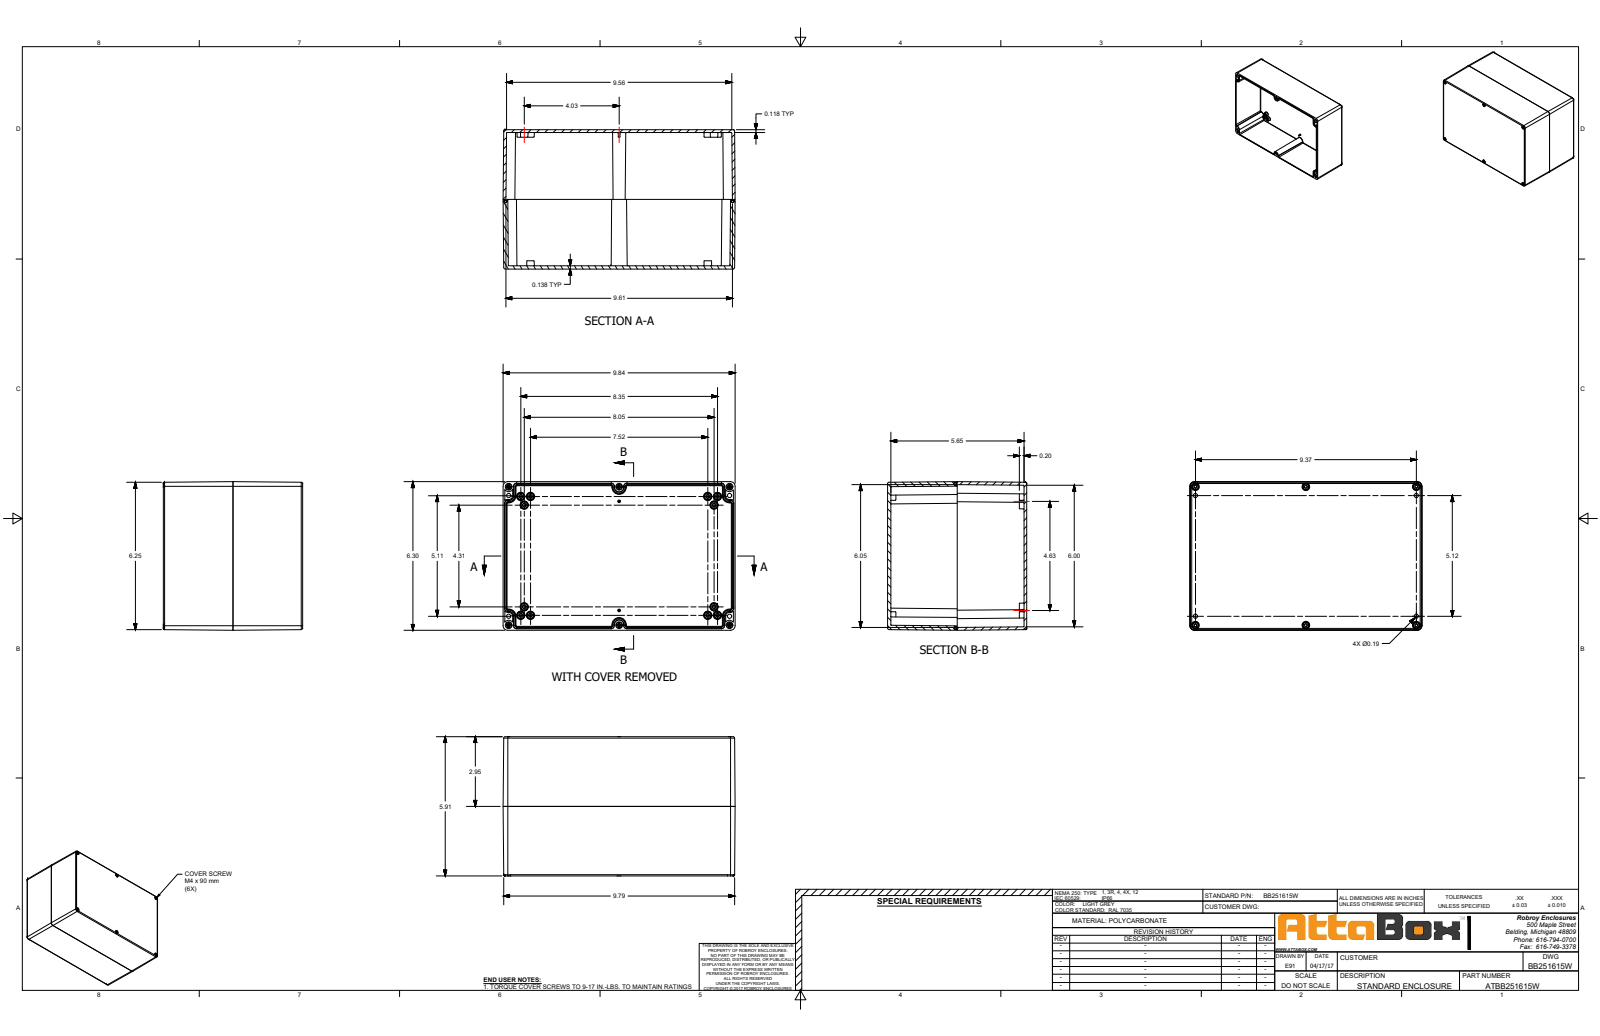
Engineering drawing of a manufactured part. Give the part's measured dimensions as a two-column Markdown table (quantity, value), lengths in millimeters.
| quantity | value |
| --- | --- |
| part name | BB251615W |
| STEP written by | SolidWorks 2018 (AUTOMOTIVE_DESIGN) |
| units | millimeters |
| bodies | 15 solids, 2307 faces (907 planar, 626 cylindrical, 774 other) |
| overall size | 250 × 160 × 150 |
| volume | 778 100 mm³ |
| surface area | 455 700 mm² |
| round holes (diameter × count) | 3.3 × 6, 4.5 × 6, 4.9 × 6, 5.1 × 6, 7 × 6, 7.2 × 6, 8.2 × 6, 4.7 × 4 |
| round bosses / shafts (diameter × count) | 4.4 × 6, 4 × 6, 3.3 × 6 |
| partial cylindrical surfaces (radius × count) | 1.2 × 40, 0.5 × 30, 1 × 20, 4.2 × 18, 1.5 × 16, 0.1 × 12, 2.6 × 6, 3.1 × 6 |
| main face-to-face distances | 3, 150, 160, 147, 3.5, 146.5, 143.5, 155.2, 156.8, 3.1 |
| hole center spacings | 9.5, 119, 119.4, 139.5, 183.4, 190.7, 238, 238.2 |
